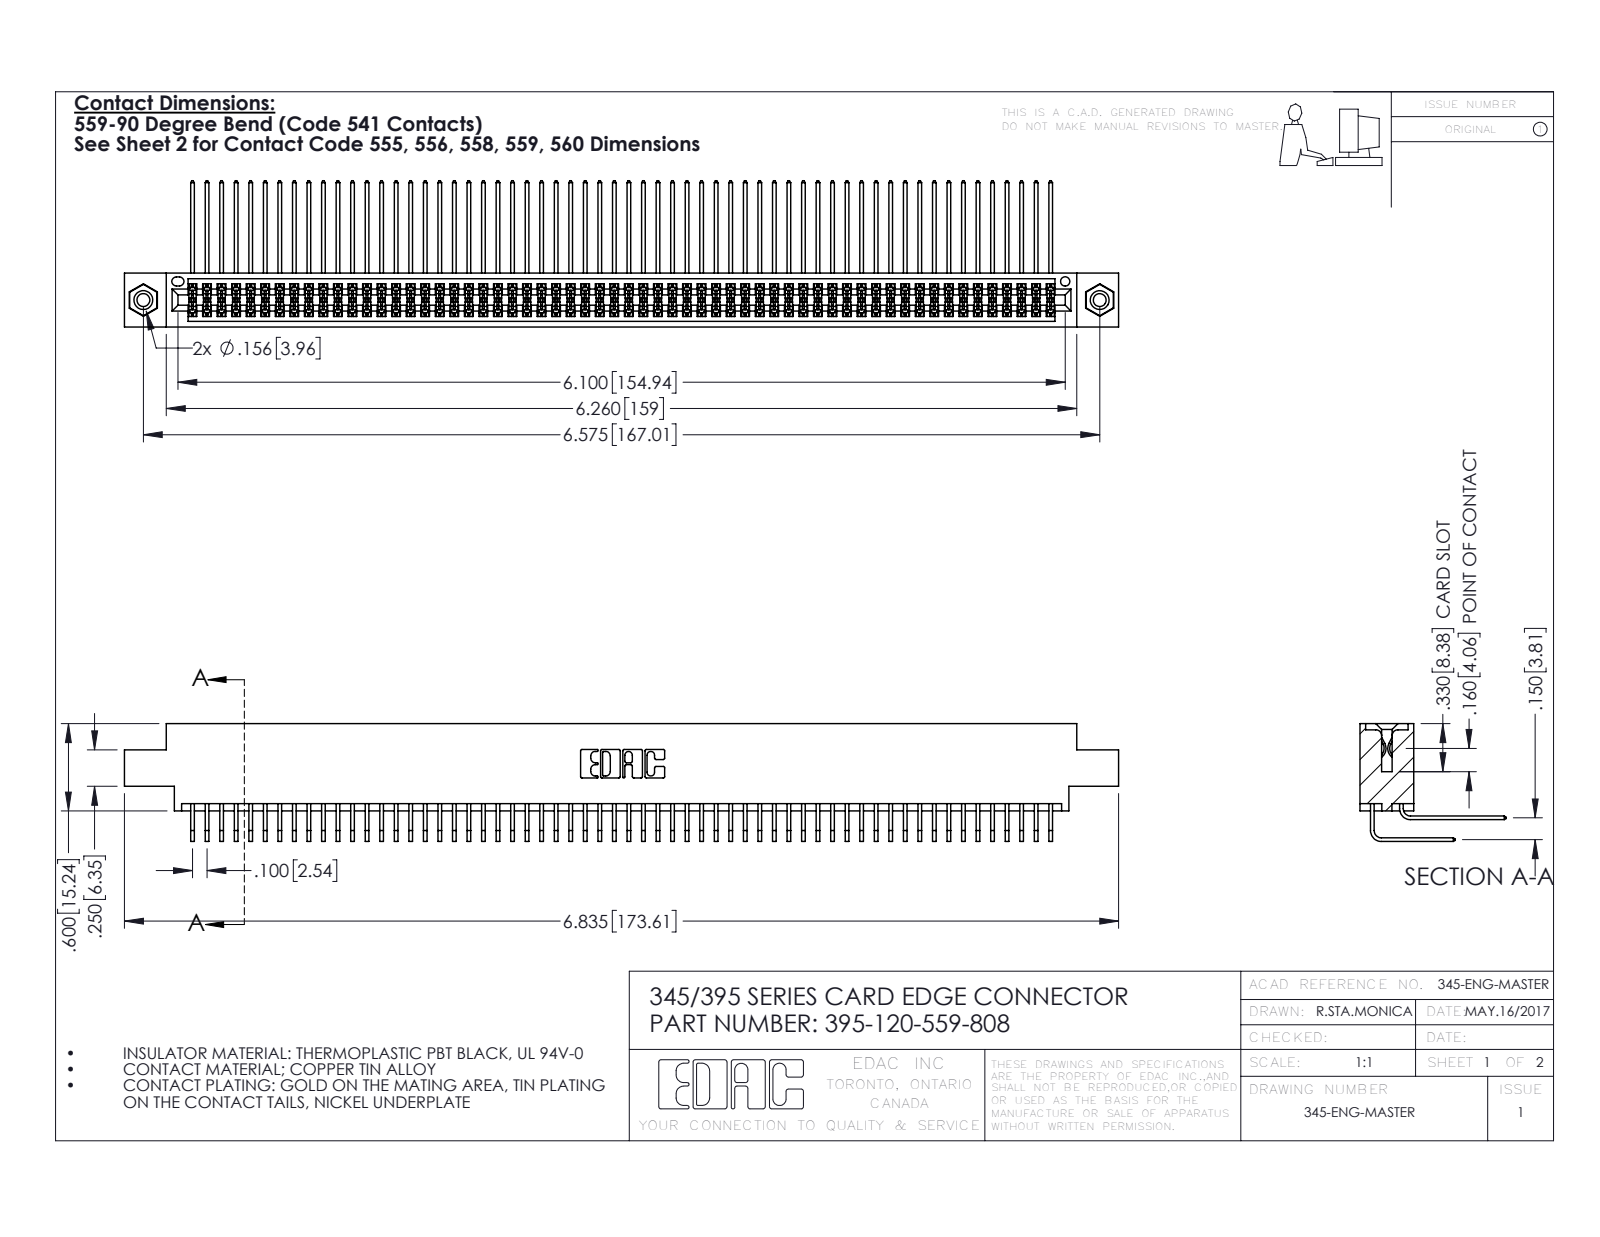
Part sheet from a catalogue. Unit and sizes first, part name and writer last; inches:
Units: inches
Overall size (bounding box): 6.835 × 1.005 × 0.809
Round holes (diameter × count): ⌀0.089 ×2, ⌀0.125 ×2, ⌀0.156 ×2, ⌀0.064 ×1
Round bosses / shafts (diameter × count): ⌀0.155 ×2
Partial cylindrical surfaces — rounded edges, fillets, slot ends (radius × count): R0.006 ×181, R0.01 ×22, R0.007 ×6, R0.031 ×6, R0.026 ×3, R0.014 ×2, R0.019 ×2, R0.022 ×2
Main face-to-face distances: 0.072, 0.298, 0.37, 0.2, 0.098, 0.272, 0.025, 0.225, 0.175, 0.15
Hole centre spacings: 0.27, 6.339, 6.575
Volume: 1.074 in³ · Surface area: 46.16 in²
Bodies: 123 solids, 6430 faces (4316 planar, 2098 cylindrical, 16 other)
Part name (STEP PRODUCT): 395-120-559-808; 345 Part_0.170 Offset - 0.156 Dia-TI; 345-292-001_559 Tail - 2; 345-292-001_558 559 Tail - 1 (+1 more)
STEP written by: SolidWorks 2016 (CONFIG_CONTROL_DESIGN)
